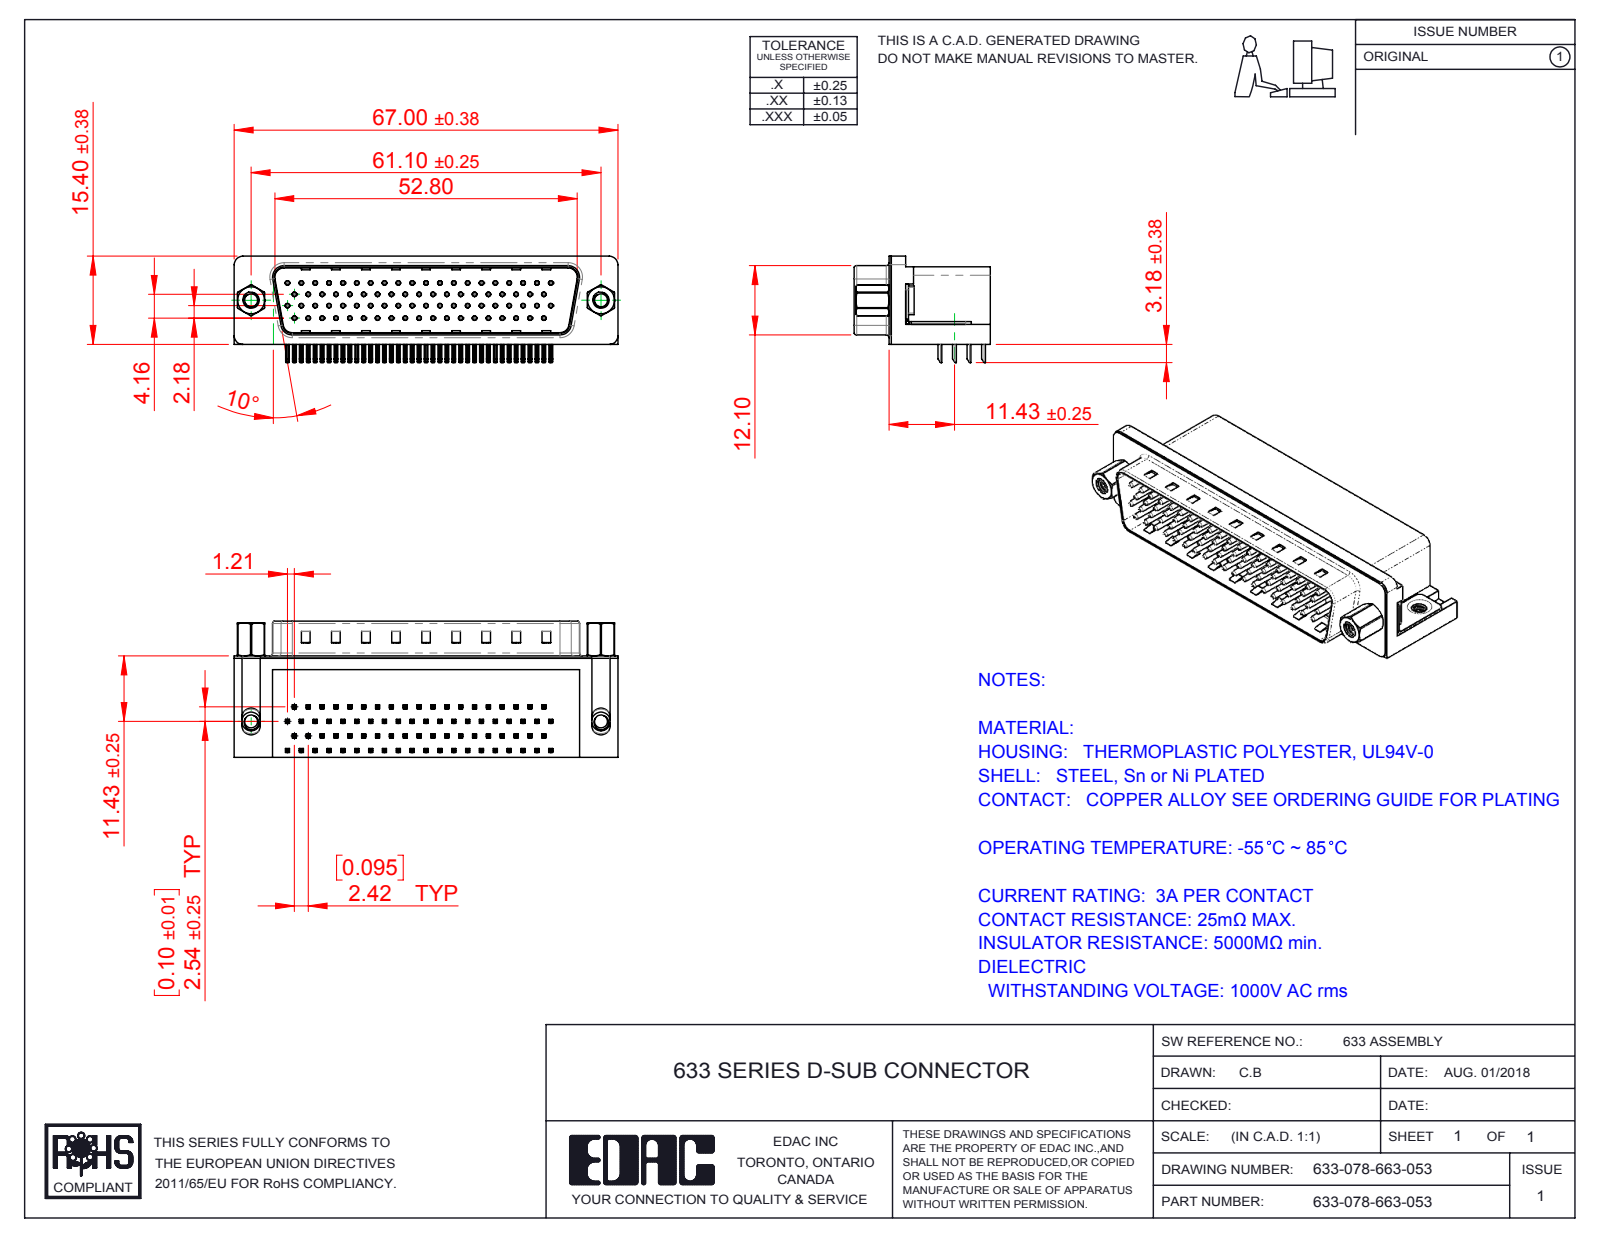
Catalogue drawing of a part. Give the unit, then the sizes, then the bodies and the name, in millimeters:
Units: millimetres
Overall size (bounding box): 67 × 23.8 × 18.58
Round holes (diameter × count): ⌀0.35 ×78, ⌀0.8 ×78, ⌀2.26 ×4, ⌀2.29 ×2, ⌀4 ×2, ⌀4.8 ×2, ⌀5 ×2
Round bosses / shafts (diameter × count): ⌀0.75 ×78, ⌀4.9 ×2, ⌀4.75 ×2, ⌀3.9 ×2, ⌀3.26 ×2, ⌀2.79 ×2
Partial cylindrical surfaces — rounded edges, fillets, slot ends (radius × count): R0.25 ×320, R0.12 ×156, R1 ×16, R0.5 ×9, R1.6 ×8, R1.5 ×6, R0.45 ×4, R0.9 ×4
Main face-to-face distances: 0.4, 13.2, 17.3, 11.7, 13.35, 2.05, 13.75, 1.65, 1.85, 11.9
Hole centre spacings: 2.42, 4.84, 7.26, 9.68, 6.26, 7.13, 12.1, 8.62
Volume: 14 826 mm³ · Surface area: 16 881 mm²
Bodies: 86 solids, 6426 faces (4003 planar, 1854 cylindrical, 569 other)
Part name (STEP PRODUCT): 633 Shell_78 Contact; 633 Contact Middle_78 Contact; 633-078-663-053; 633 4-40 Threaded Rivet (+6 more)
STEP written by: SolidWorks 2016 (CONFIG_CONTROL_DESIGN)
